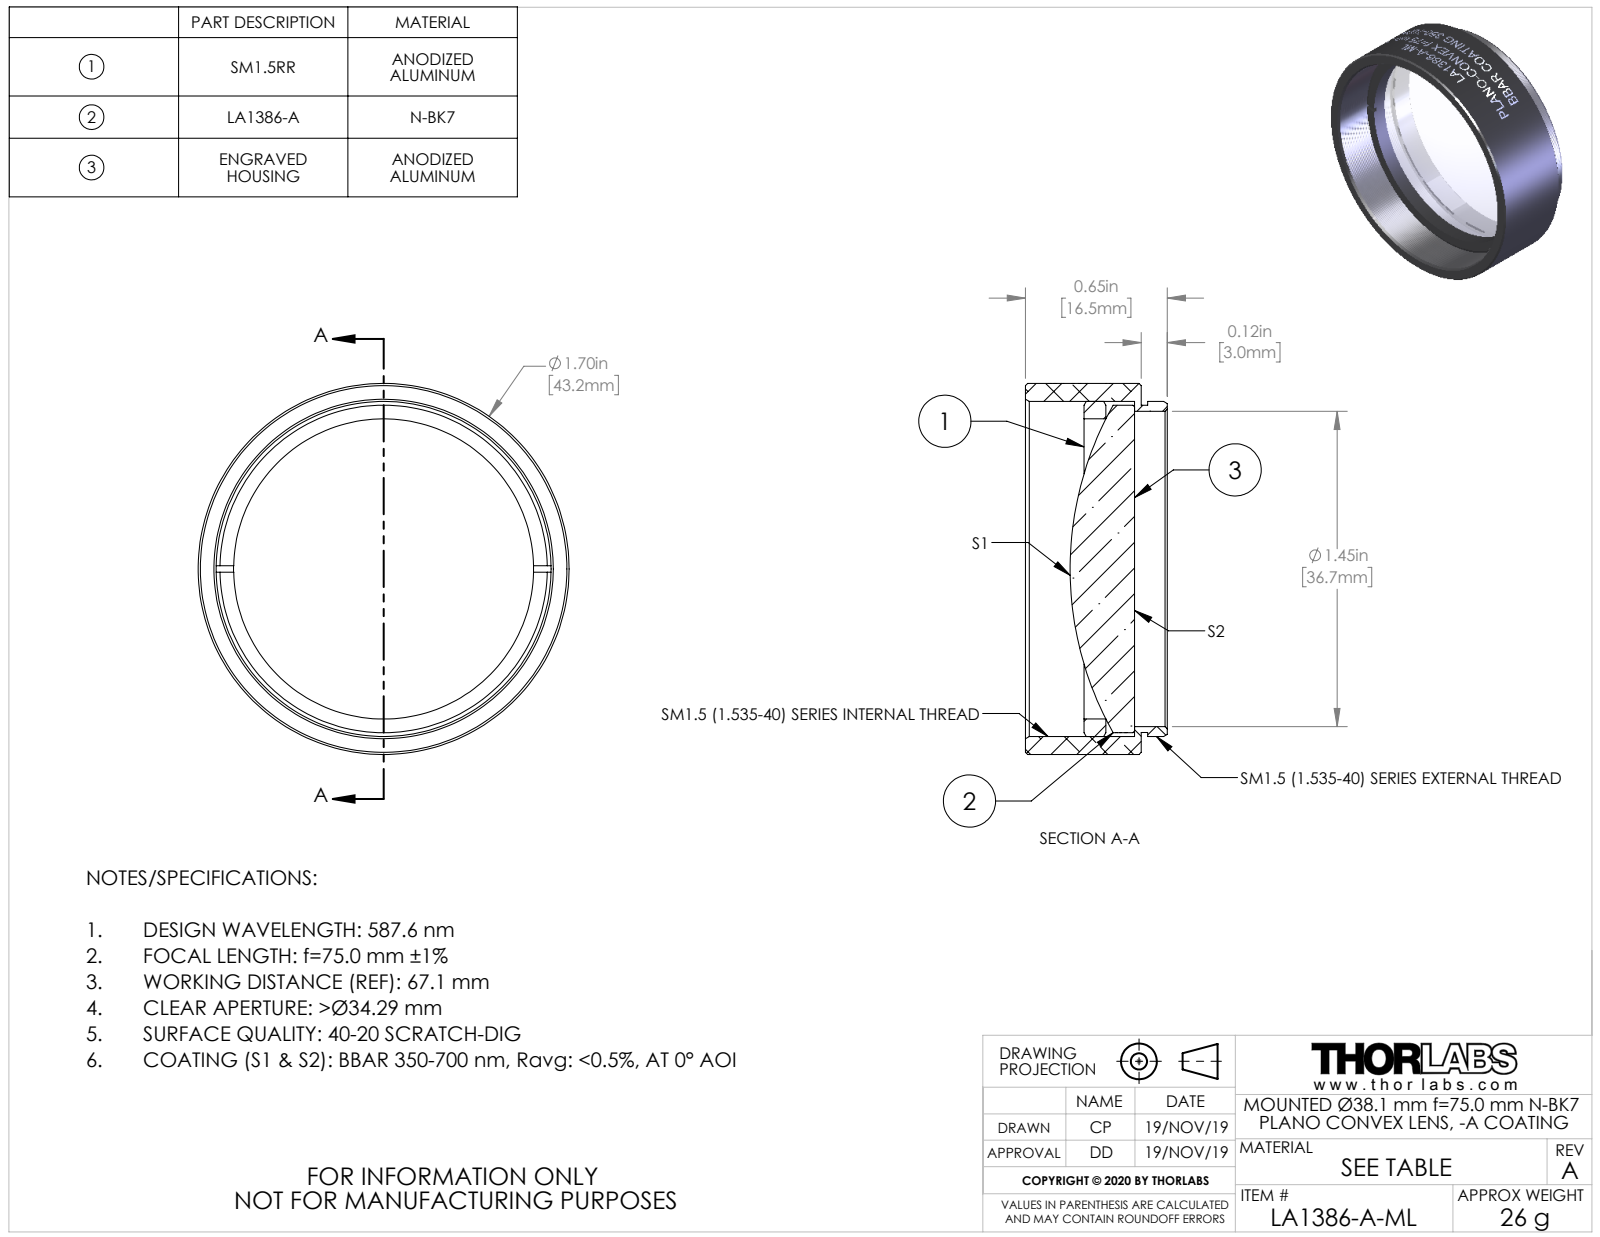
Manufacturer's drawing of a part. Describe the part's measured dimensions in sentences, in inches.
The part is named "TTN200719-E0W". Its 3-D file was written by "SolidWorks 2018 (CONFIG_CONTROL_DESIGN)". It is 3 solids with 156 faces: 15 planar, 122 cylindrical and 19 other. Overall it measures 1.7 by 1.7 by 0.65 inches. Its volume is 0.637 cubic inches and its surface area 13.45 square inches. Round holes: 1 of diameter 1.375, 1 of diameter 1.445. Round bosses or shafts: 1 of diameter 1.7, 1 of diameter 1.535, 1 of diameter 1.5, 1 of diameter 1.499. The main face-to-face distances are 0.03, 0.53, 0.5, 0.162, 0.131, 0.369, 0.262, 0.231, 0.1, 0.269.
